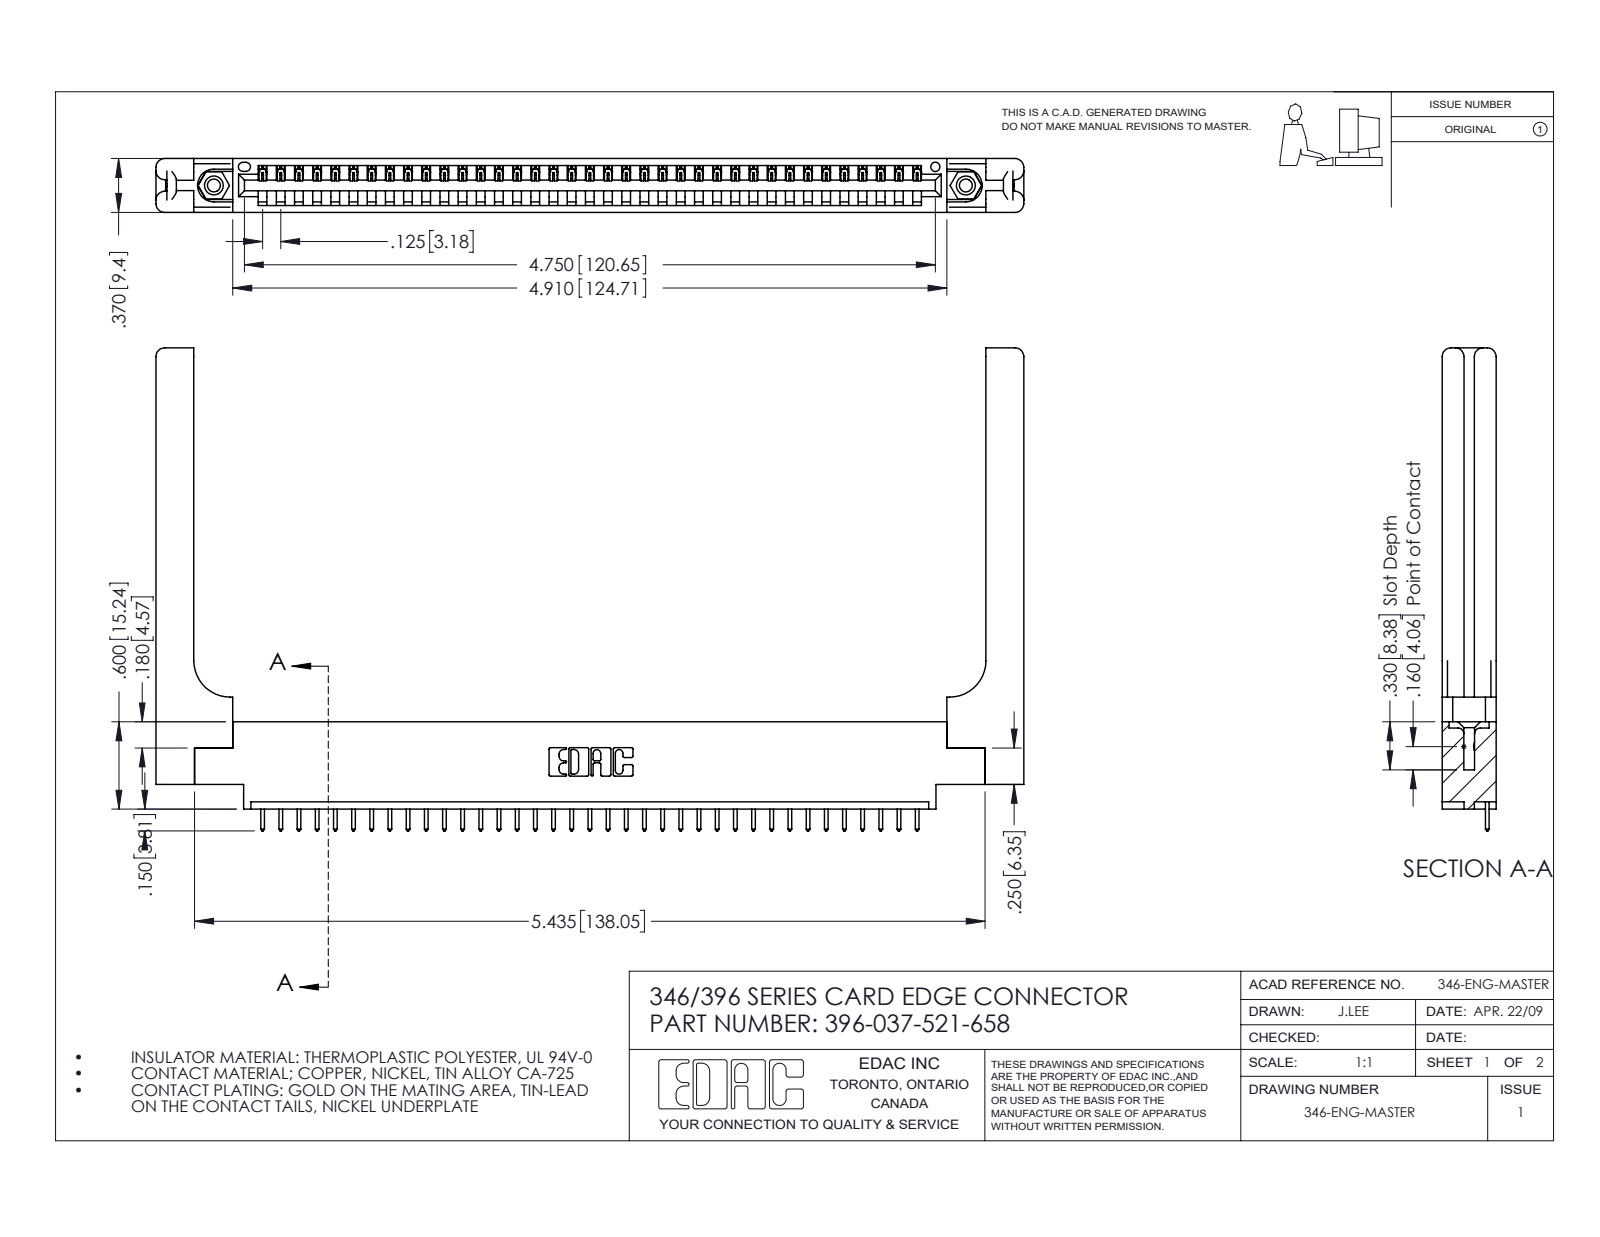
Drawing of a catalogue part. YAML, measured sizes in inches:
part_name: "396-037-521-658; 346-220-058_345-220-058; 345-250-001_345-250-001-102; 346 Part_0.170 Offset - 0.156 Dia-TH (+1 more)"
step_written_by: "SolidWorks 2016 (CONFIG_CONTROL_DESIGN)"
units: inches
bodies: {solids: 42, faces: 2528, planar: 1708, cylindrical: 760, other: 60}
overall_size: [5.966, 3.32, 0.37]
volume: 1.326
surface_area: 35.06
round_holes:
  - {diameter: 0.089, count: 2}
  - {diameter: 0.125, count: 2}
  - {diameter: 0.156, count: 2}
  - {diameter: 0.064, count: 1}
round_bosses_or_shafts:
  - {diameter: 0.155, count: 2}
partial_cylinders:
  - {radius: 0.006, count: 74}
  - {radius: 0.01, count: 74}
  - {radius: 0.01, count: 22}
  - {radius: 0.06, count: 16}
  - {radius: 0.007, count: 6}
  - {radius: 0.031, count: 6}
  - {radius: 0.026, count: 3}
  - {radius: 0.03, count: 2}
face_to_face_distances: [0.37, 0.048, 0.322, 0.072, 0.148, 0.15, 0.25, 0.298, 0.025, 0.222]
hole_center_spacings: [0.246, 4.961, 5.17]
